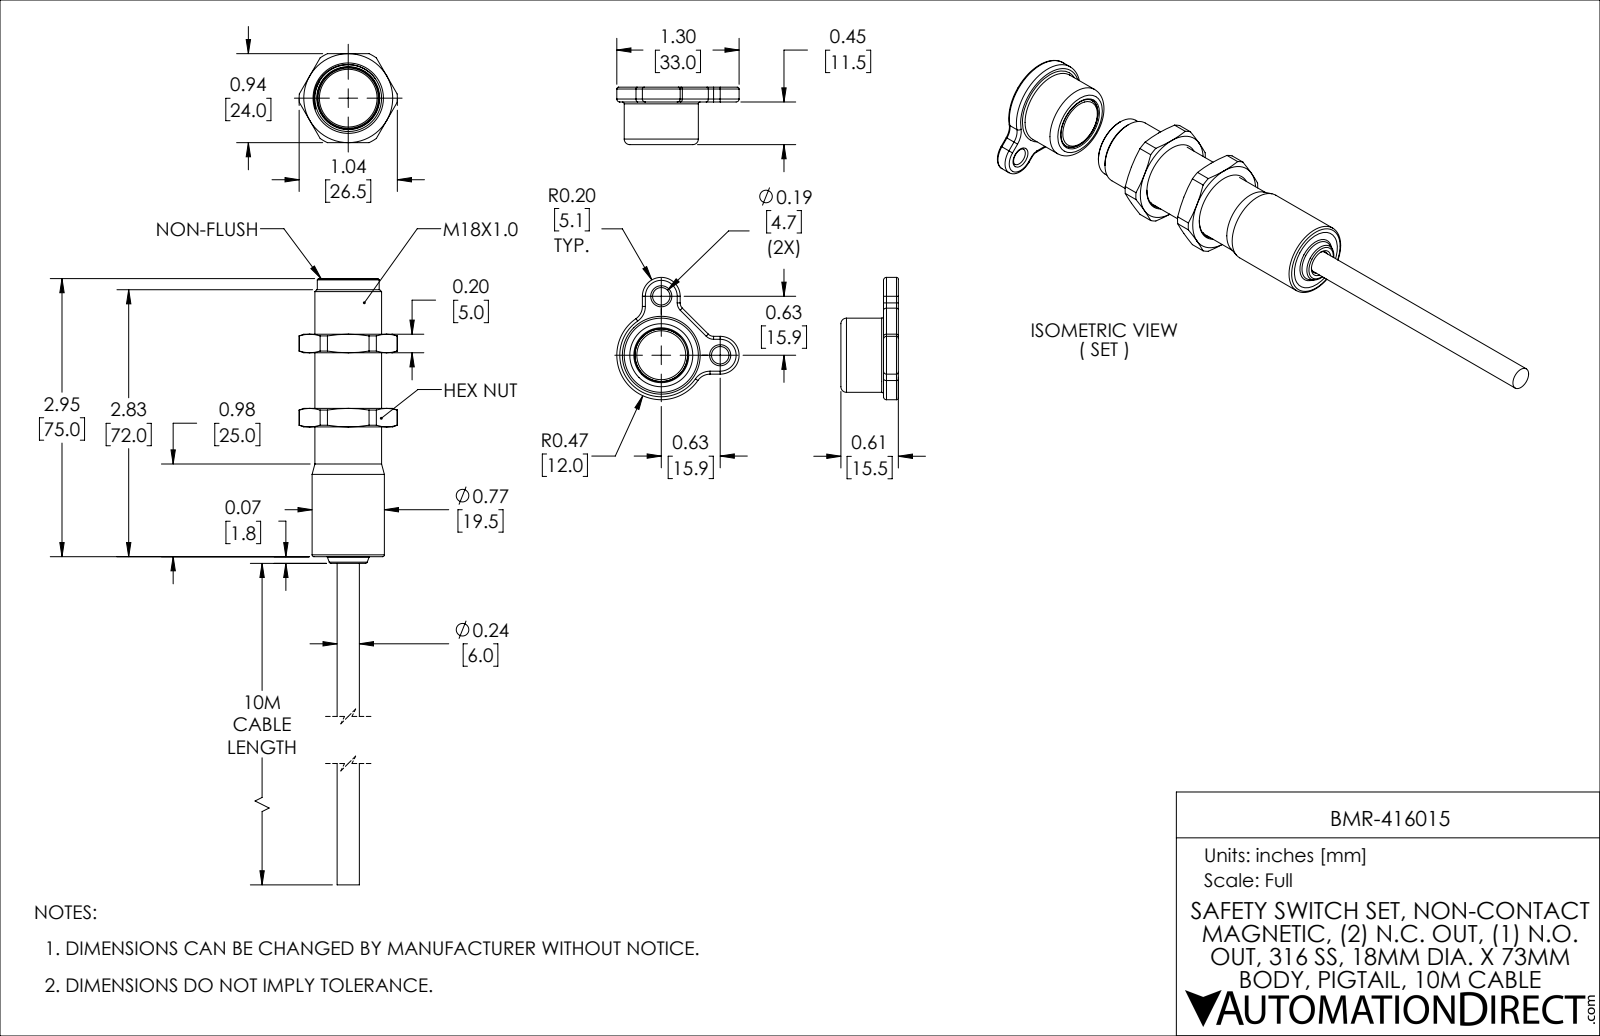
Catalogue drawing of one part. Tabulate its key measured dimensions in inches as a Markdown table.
| quantity | value |
| --- | --- |
| part name | 416-BMR |
| STEP written by | SolidWorks 2019 (AUTOMOTIVE_DESIGN) |
| units | inches |
| bodies | 4 solids, 167 faces (39 planar, 49 cylindrical, 79 other) |
| overall size | 7.232 × 1.287 × 1.116 |
| volume | 1.754 in³ |
| surface area | 20.73 in² |
| round holes (diameter × count) | 0.185 × 2, 0.098 × 1, 0.252 × 1, 0.472 × 1, 0.512 × 1, 0.535 × 1, 0.559 × 1, 0.673 × 1, 0.803 × 1 |
| round bosses / shafts (diameter × count) | 0.787 × 1, 0.768 × 1, 0.709 × 1, 0.661 × 1, 0.657 × 1, 0.618 × 1, 0.591 × 1, 0.236 × 1 |
| partial cylindrical surfaces (radius × count) | 0.02 × 5, 0.031 × 5, 0.079 × 2, 0.157 × 2, 0.201 × 2, 0.472 × 1, 0.522 × 1 |
| main face-to-face distances | 0.591, 0.787, 1.378, 0.079, 0.945, 0.197, 1.575, 2.165, 0.984, 0.594 |
| hole center spacings | 0.626, 0.885 |
